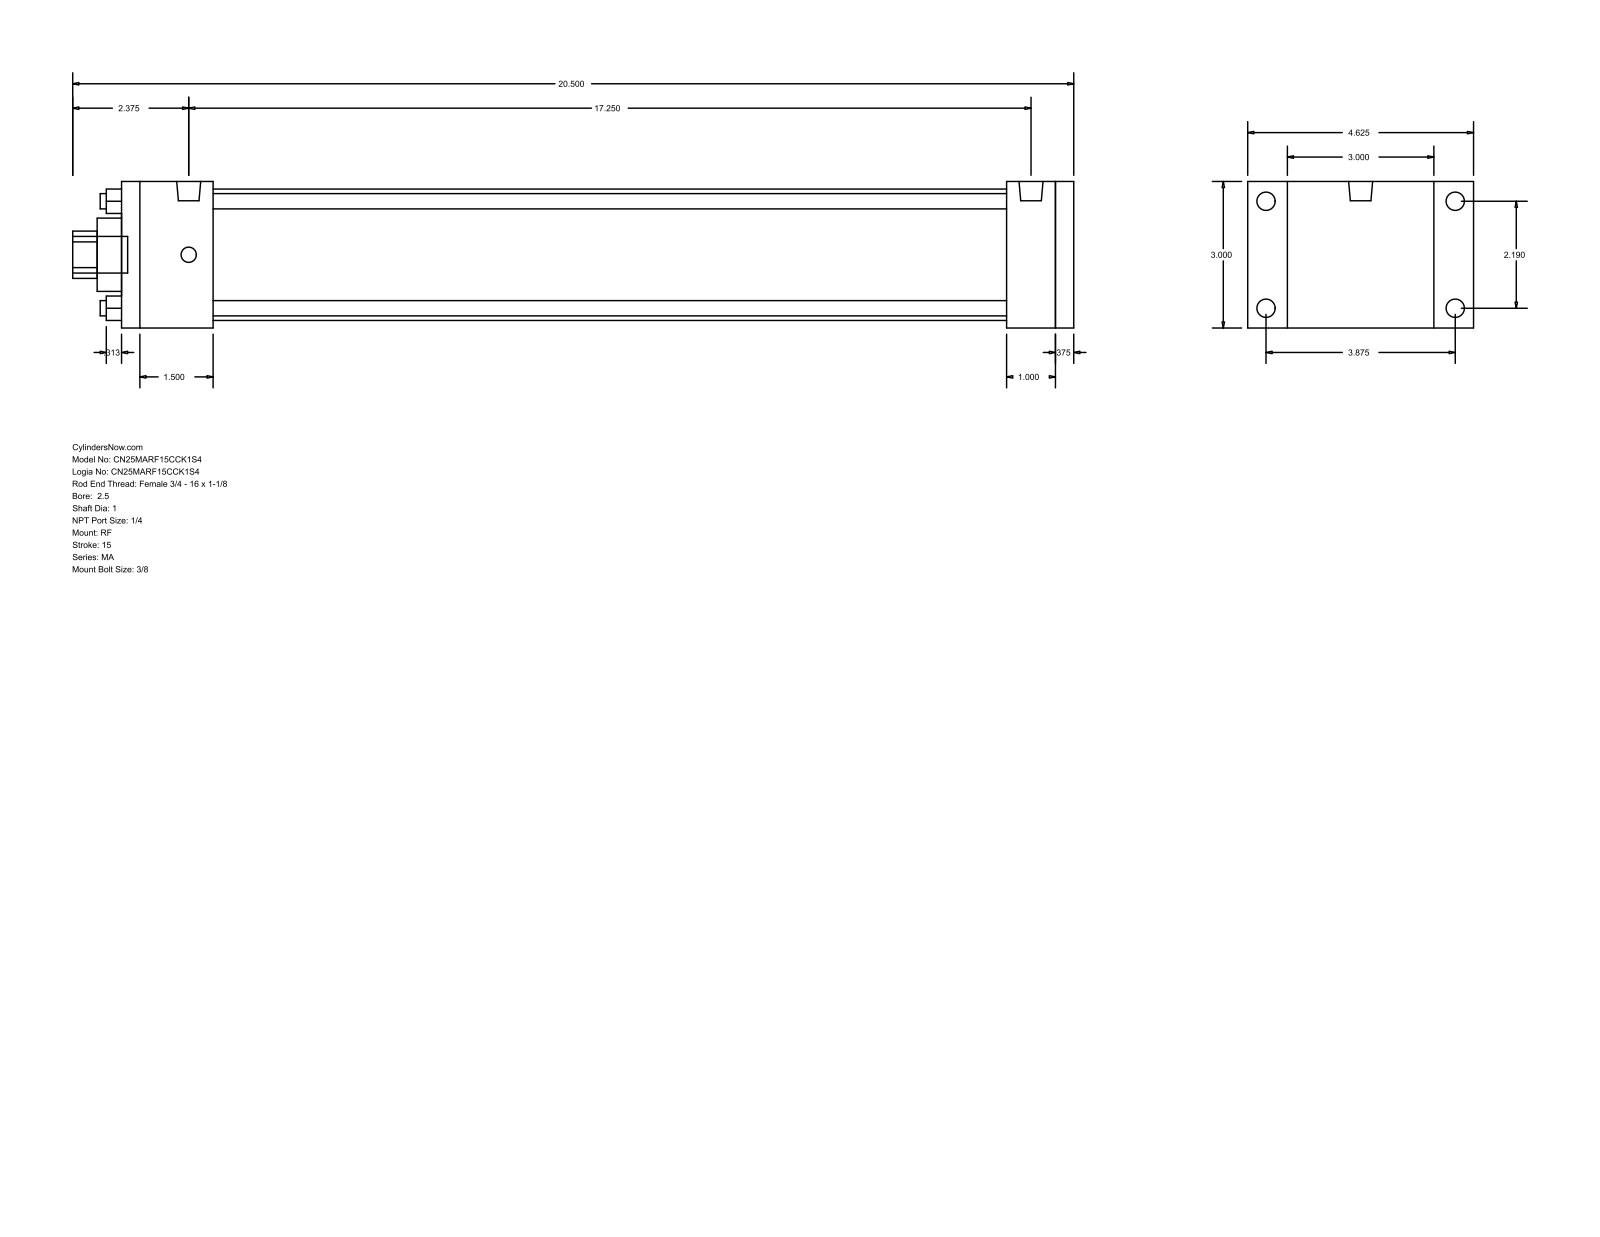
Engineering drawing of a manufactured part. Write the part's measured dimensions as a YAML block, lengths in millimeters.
part_name: "MA_RF__0250_1"
step_written_by: "GSSL Pune (CONFIG_CONTROL_DESIGN)"
units: millimeters
bodies: {solids: 0, faces: 92, planar: 64, cylindrical: 28, other: 0}
overall_size: [520.7, 117.47, 76.2]
round_holes:
  - {diameter: 7.94, count: 4}
  - {diameter: 25.4, count: 1}
  - {diameter: 38.1, count: 1}
  - {diameter: 68.33, count: 1}
round_bosses_or_shafts:
  - {diameter: 9.53, count: 4}
  - {diameter: 7.94, count: 4}
  - {diameter: 12.49, count: 2}
  - {diameter: 19.05, count: 1}
partial_cylinders:
  - {radius: 12.29, count: 1}
face_to_face_distances: [76.2, 495.3, 485.78, 9.52, 47.63, 460.37, 412.74, 438.15, 447.67, 25.41]
hole_center_spacings: [39.33, 55.62, 78.66]
